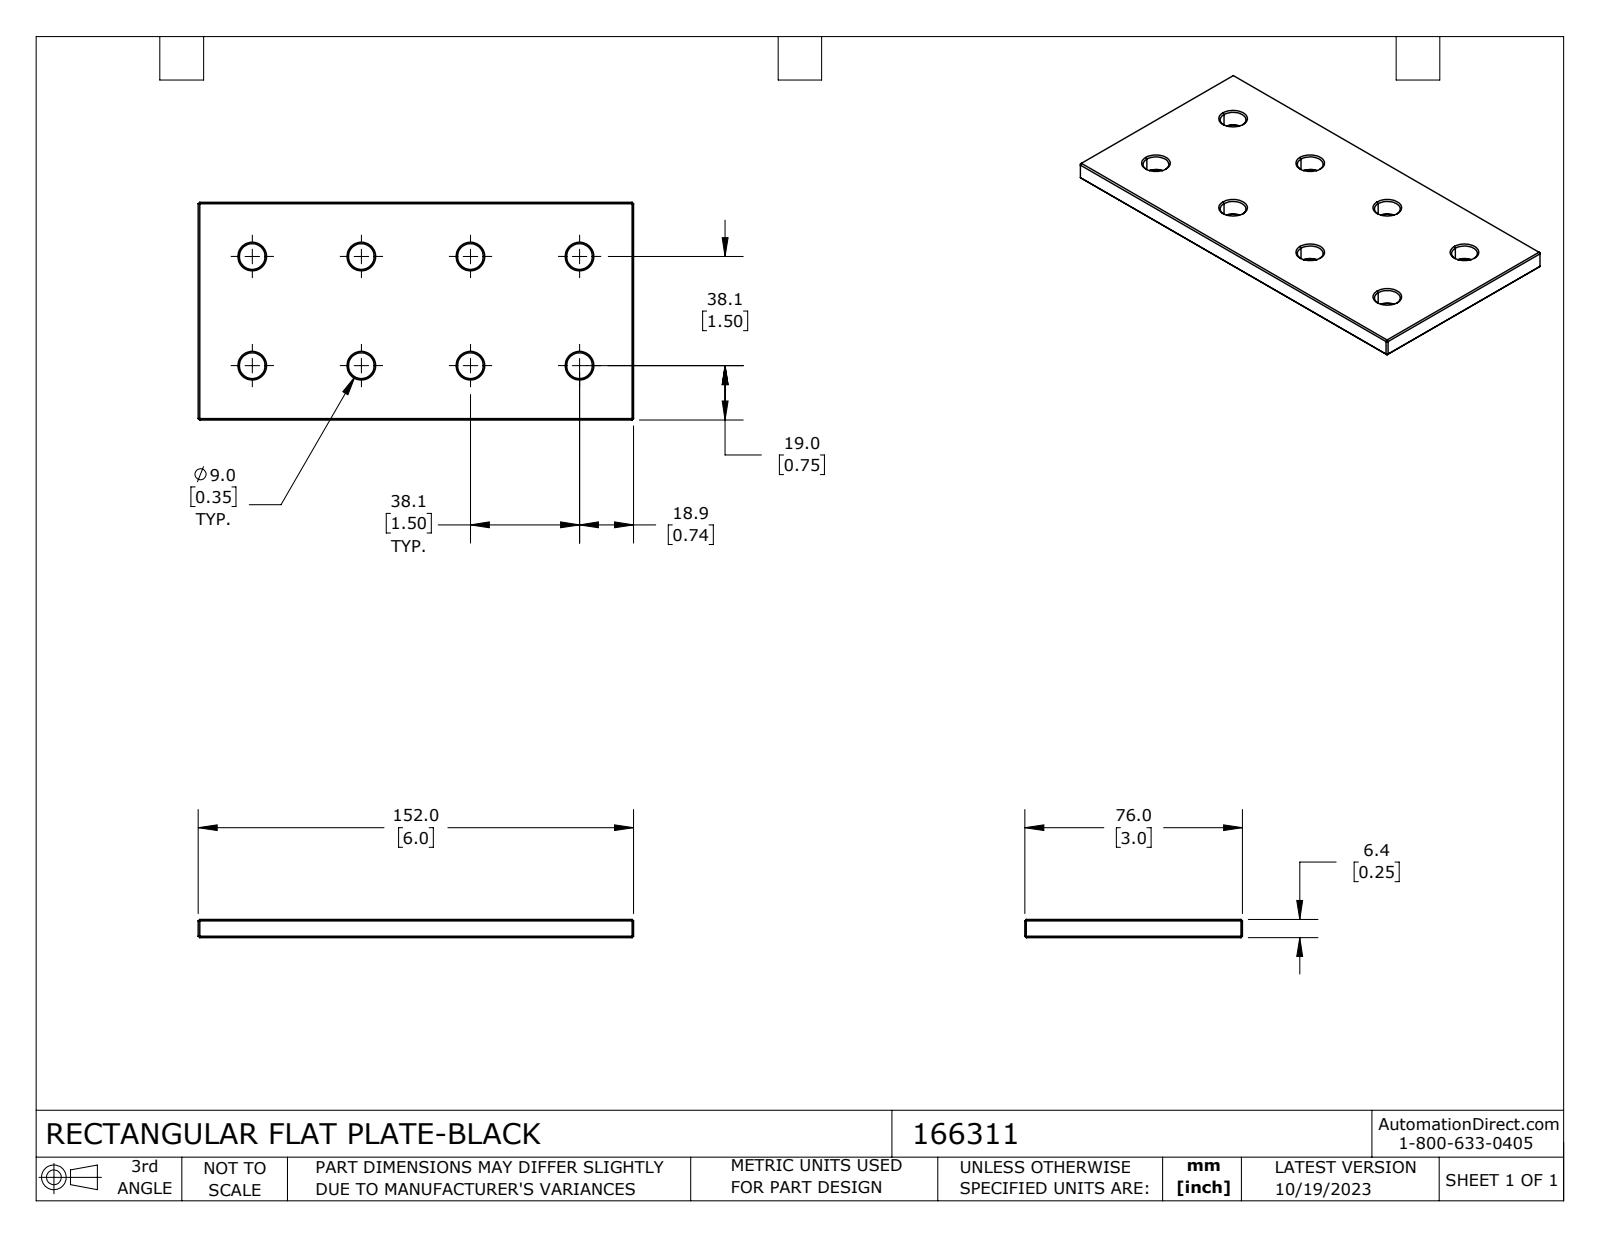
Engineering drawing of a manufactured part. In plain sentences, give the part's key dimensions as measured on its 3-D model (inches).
The part is named "166311". Its 3-D file was written by "SolidWorks 2023 (CONFIG_CONTROL_DESIGN)". It is 1 solid with 74 faces: 26 planar, 16 cylindrical and 32 other. Overall it measures 5.984 by 2.992 by 0.25 inches. Its volume is 4.268 cubic inches and its surface area 40.32 square inches. Round holes: 8 of diameter 0.354. The main face-to-face distances are 0.25, 2.992, 5.984, 2.264, 4.38, 6.318, 5.278. The hole center spacings are 1.5, 2.121, 3, 3.354, 4.5, 4.743.
